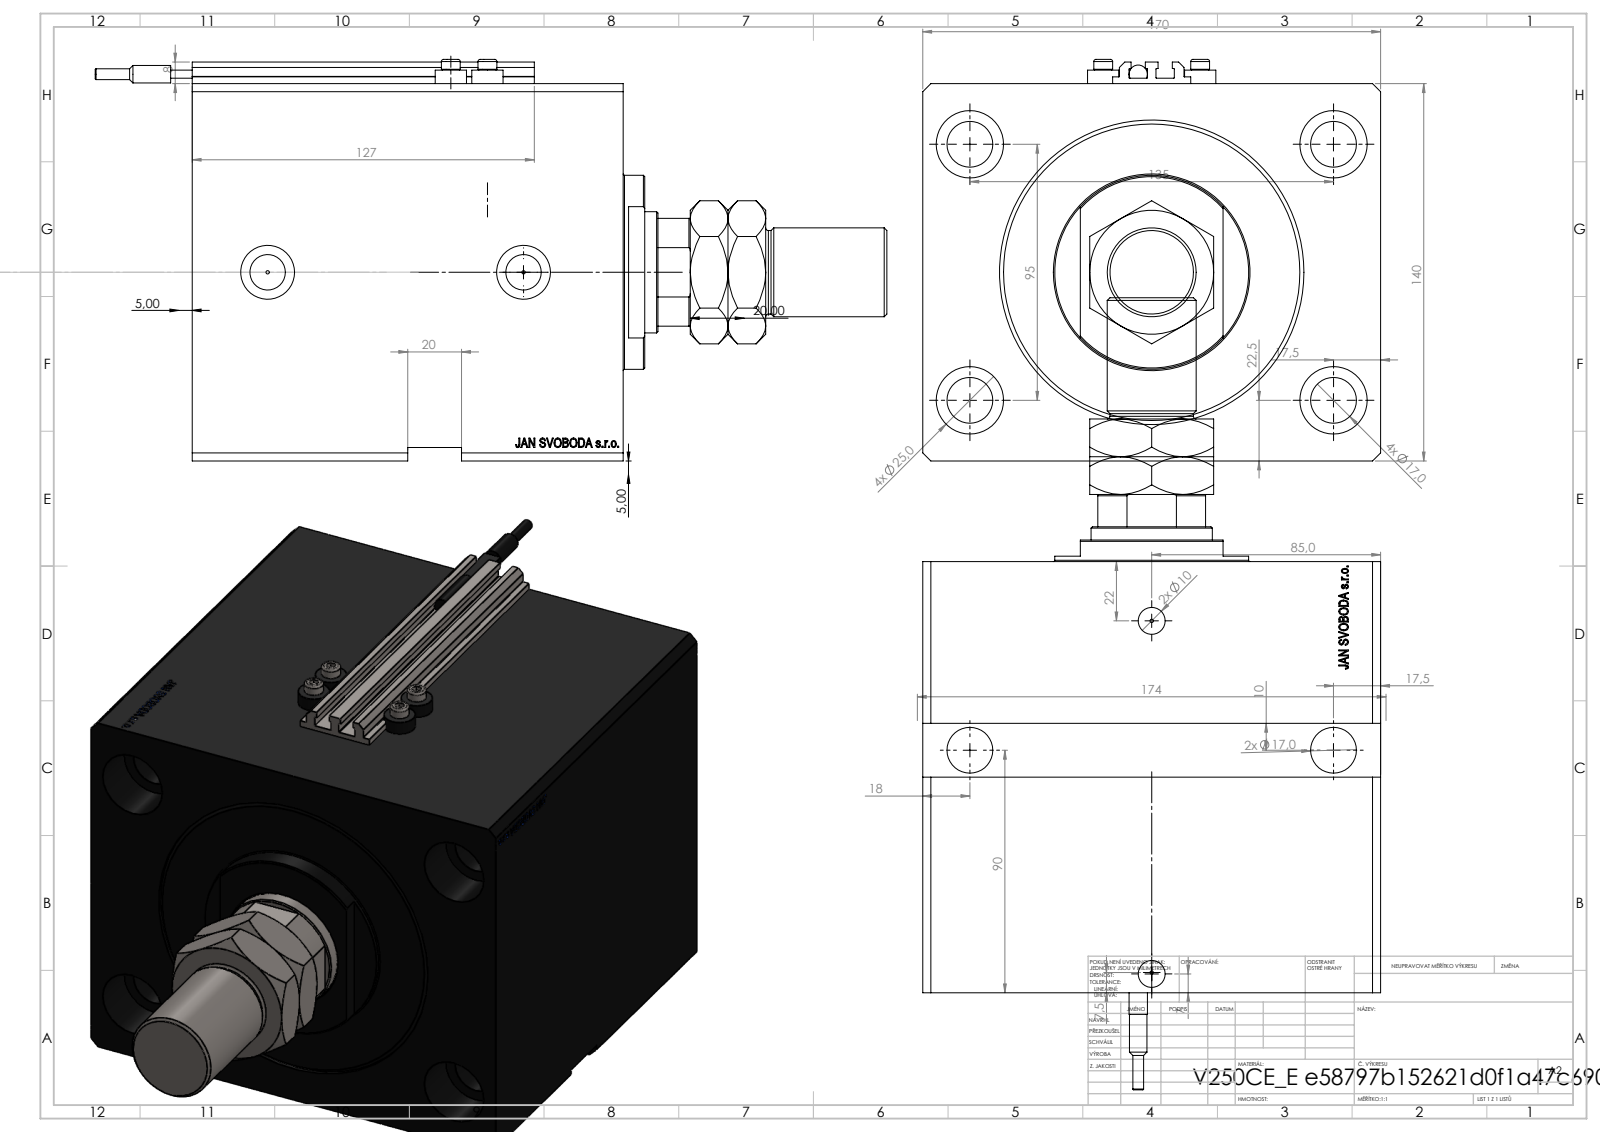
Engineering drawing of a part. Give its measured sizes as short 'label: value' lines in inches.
name: V250CE_E_Body; MTA; SWITCH_V250CE; V250CE_C_VCP (+2 more)
written by: SolidWorks 2019 (CONFIG_CONTROL_DESIGN)
unit: in
bodies: 10 solids, 1198 faces (578 planar, 148 cylindrical, 472 other)
size: 11.575 × 6.693 × 5.866
volume: 202.7 in³; area: 555 in²
holes: 8× ⌀0.669, 4× ⌀0.049, 4× ⌀0.157, 4× ⌀0.984, 2× ⌀0.394, 2× ⌀0.518, 2× ⌀0.787, 1× ⌀1.24, 1× ⌀1.772, 1× ⌀3.937, 1× ⌀4.449
bosses: 4× ⌀0.457, 4× ⌀0.276, 1× ⌀2.835, 1× ⌀1.299, 1× ⌀1.22, 1× ⌀0.268, 1× ⌀0.256, 1× ⌀0.157
rounds: 10× R0.008, 1× R0.866
face distances: 5.512, 6.693, 6.299, 1.138, 5.161, 0.984, 5.315, 4.177, 1.969, 3.346
hole spacings: 3.25, 5.315, 3.74, 0.535, 1.181, 1.324, 1.417, 1.515
